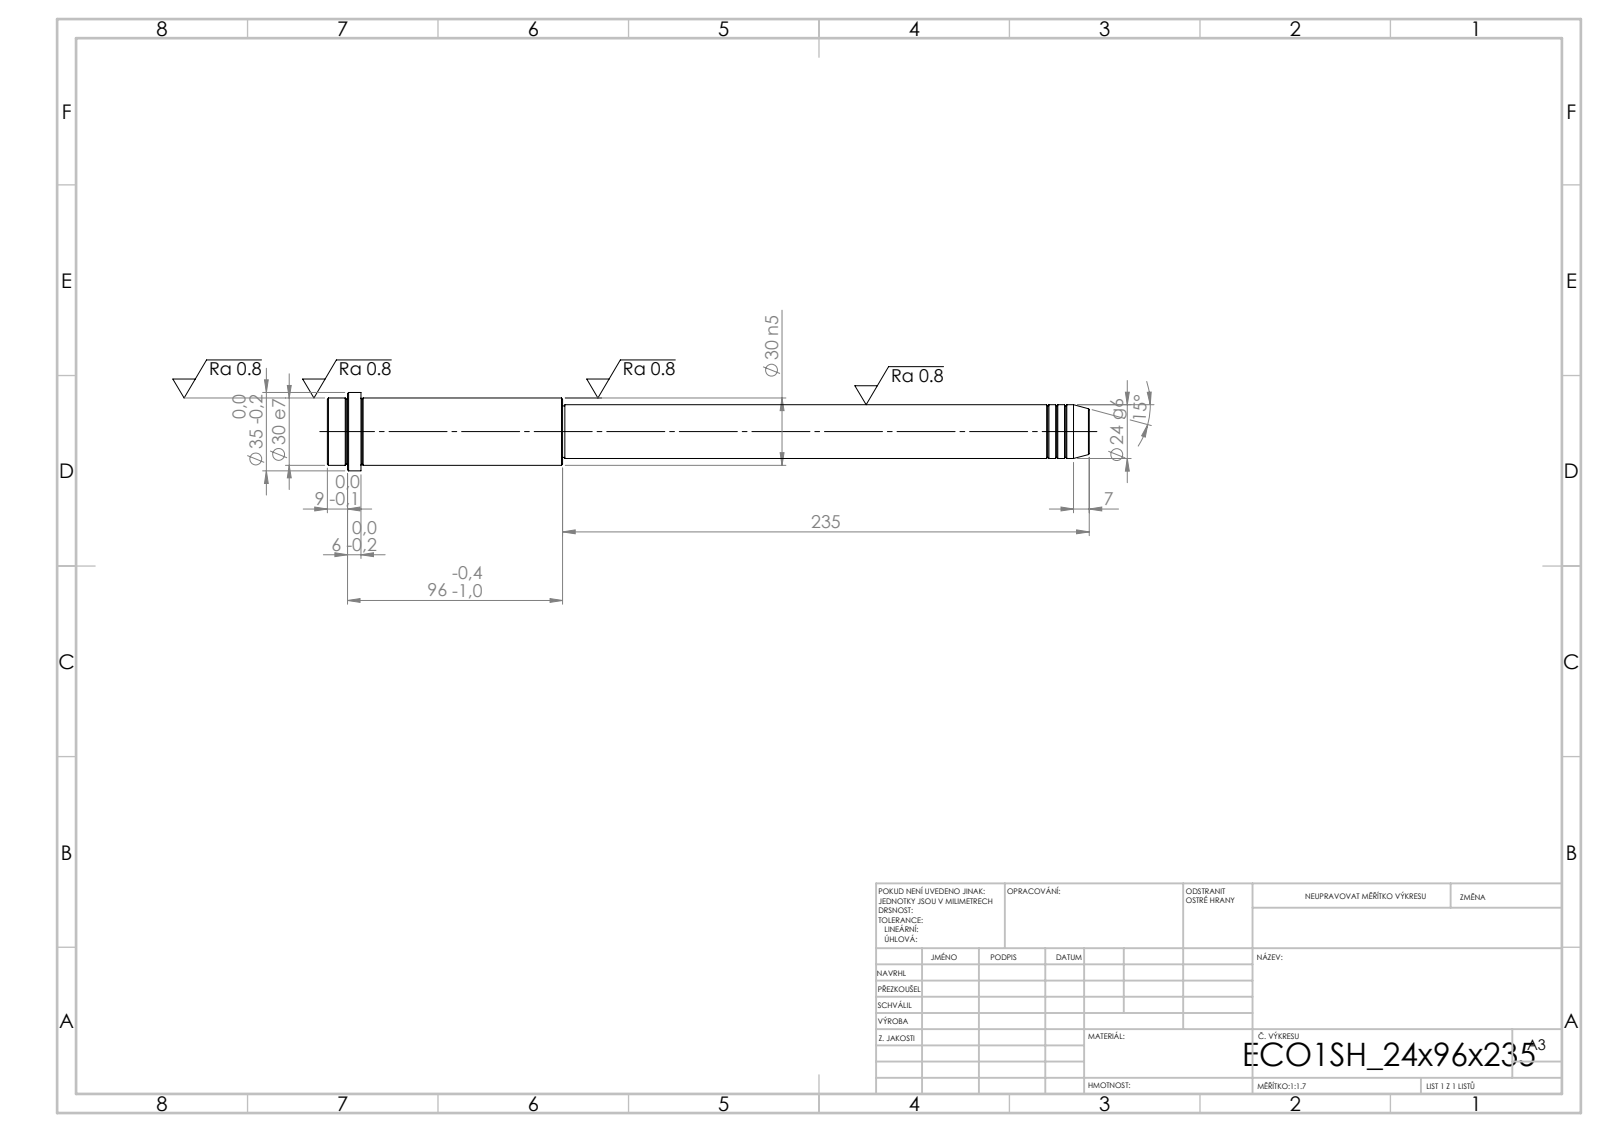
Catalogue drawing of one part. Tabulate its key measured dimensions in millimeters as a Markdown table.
| quantity | value |
| --- | --- |
| STEP written by | SolidWorks 2019 (CONFIG_CONTROL_DESIGN) |
| units | millimeters |
| bodies | 1 solid, 52 faces (6 planar, 16 cylindrical, 30 other) |
| overall size | 340 × 35 × 35 |
| volume | 181 358 mm³ |
| surface area | 29 675 mm² |
| round bosses / shafts (diameter × count) | 35 × 1, 30 × 1, 24 × 1, 23 × 1 |
| main face-to-face distances | 340, 325, 15, 235, 90, 105, 331, 96, 6, 9 |
